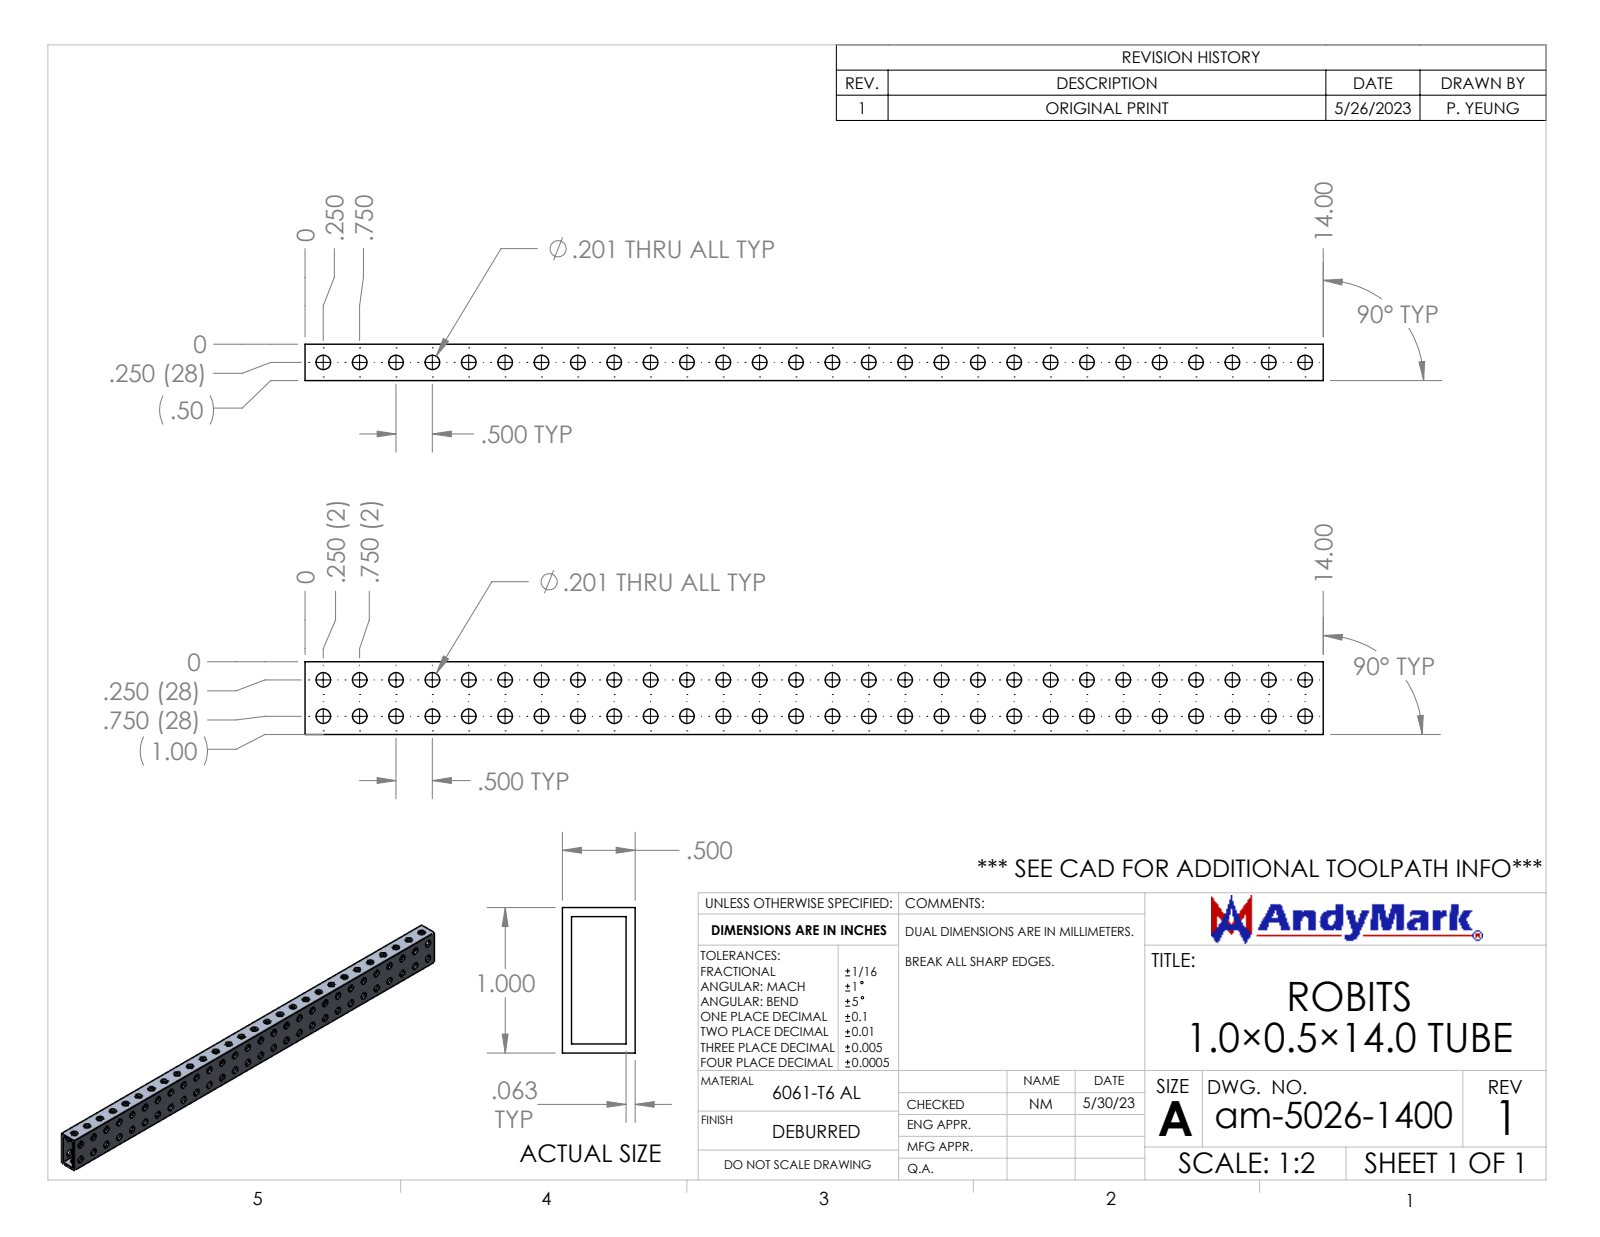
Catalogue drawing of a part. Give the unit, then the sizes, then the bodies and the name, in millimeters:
Units: millimetres
Overall size (bounding box): 355.6 × 25.4 × 12.7
Round holes (diameter × count): ⌀5.1 ×84
Main face-to-face distances: 1.6, 11.1, 12.7, 9.5, 23.8, 25.4, 22.2, 355.6
Hole centre spacings: 12.7, 25.4, 38.1, 50.8, 63.5, 76.2, 88.9, 101.6
Volume: 33 970 mm³ · Surface area: 47 300 mm²
Bodies: 1 solid, 346 faces (10 planar, 336 cylindrical, 0 other)
Part name (STEP PRODUCT): am-5026-1400 RoBits 1.0x0.5x14.0 Tube
STEP written by: SolidWorks 2022 (CONFIG_CONTROL_DESIGN)
